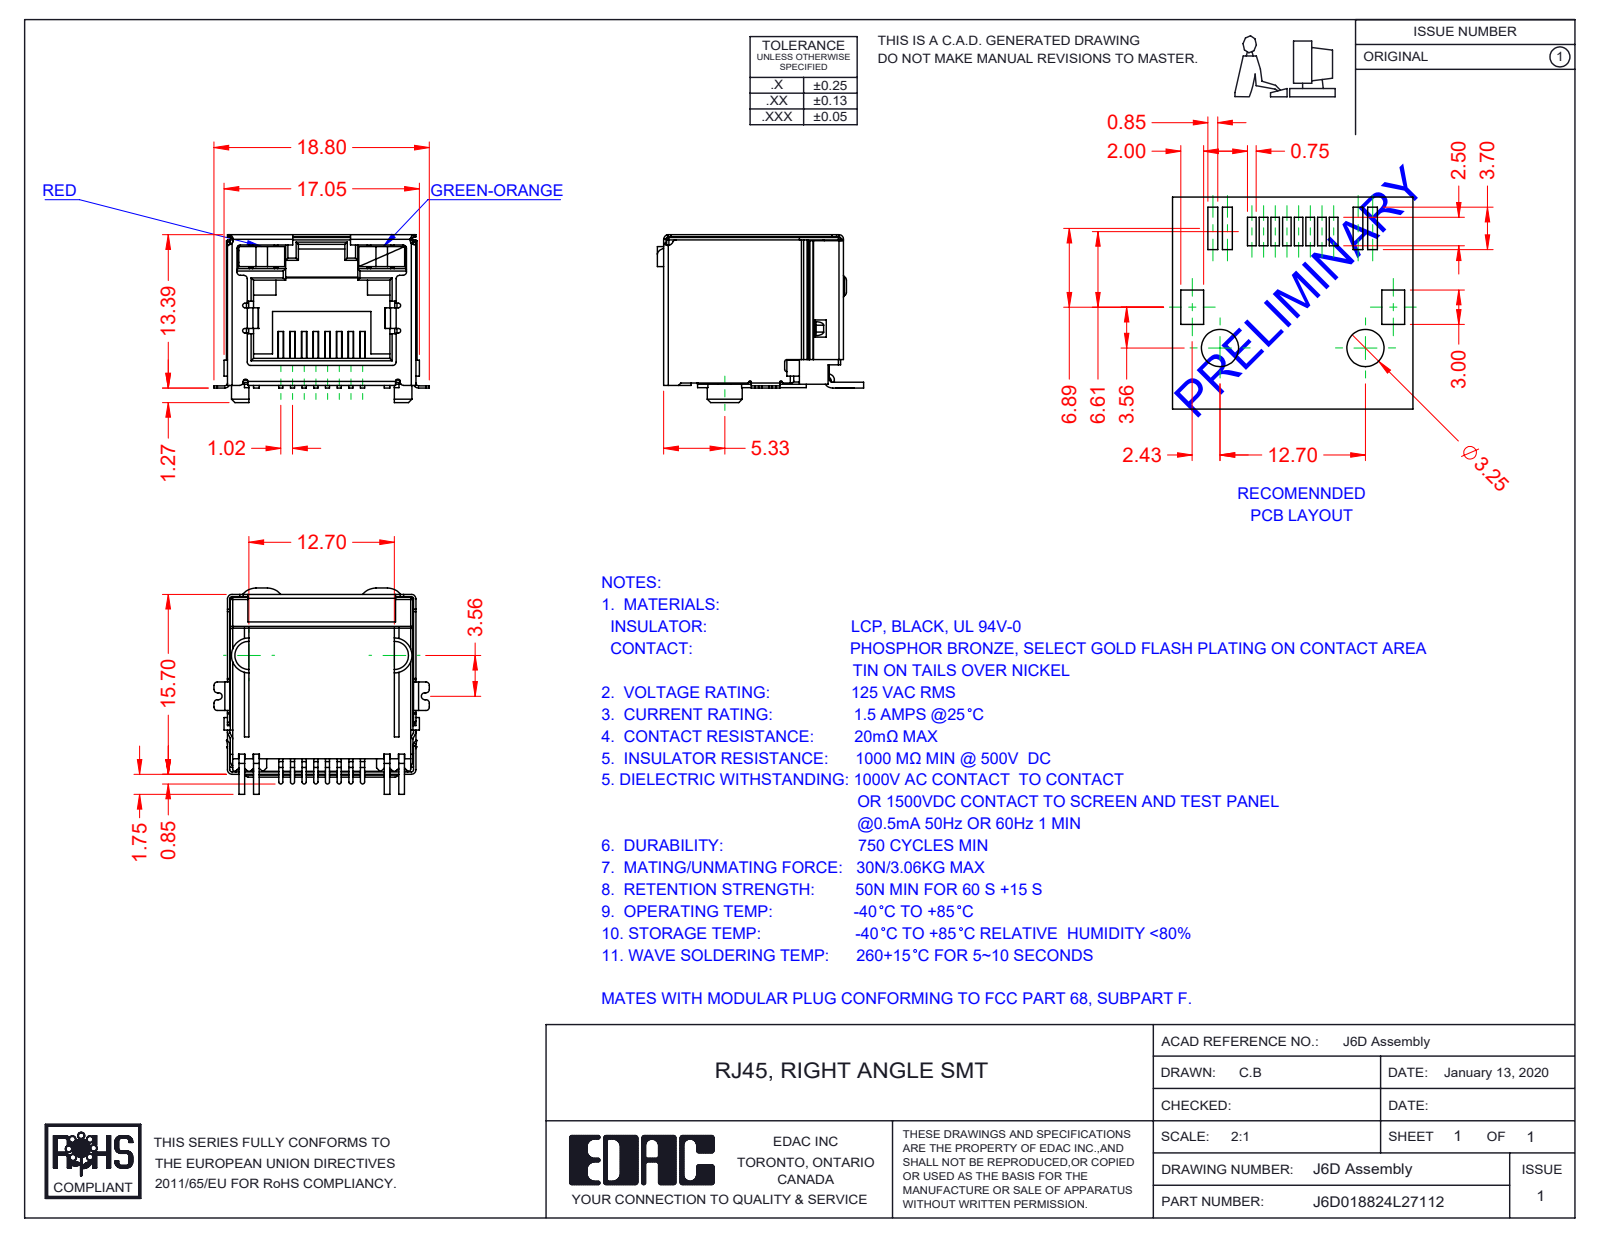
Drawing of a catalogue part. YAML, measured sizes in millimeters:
part_name: "6D Contacts; J6D018824L27112; 6D LED RH_7-Green-Orange; 6D Insulator (+2 more)"
step_written_by: "SolidWorks 2016 (CONFIG_CONTROL_DESIGN)"
units: millimeters
bodies: {solids: 12, faces: 896, planar: 645, cylindrical: 218, other: 33}
overall_size: [18.8, 18, 14.65]
volume: 1804
surface_area: 4898
partial_cylinders:
  - {radius: 0.3, count: 39}
  - {radius: 0.2, count: 37}
  - {radius: 0.4, count: 16}
  - {radius: 0.1, count: 12}
  - {radius: 0.15, count: 8}
  - {radius: 0.18, count: 8}
  - {radius: 0.5, count: 6}
  - {radius: 1.5, count: 5}
face_to_face_distances: [16, 16.25, 16.2, 2.25, 1, 15.95, 16.05, 12.8, 0.45, 16.45]
